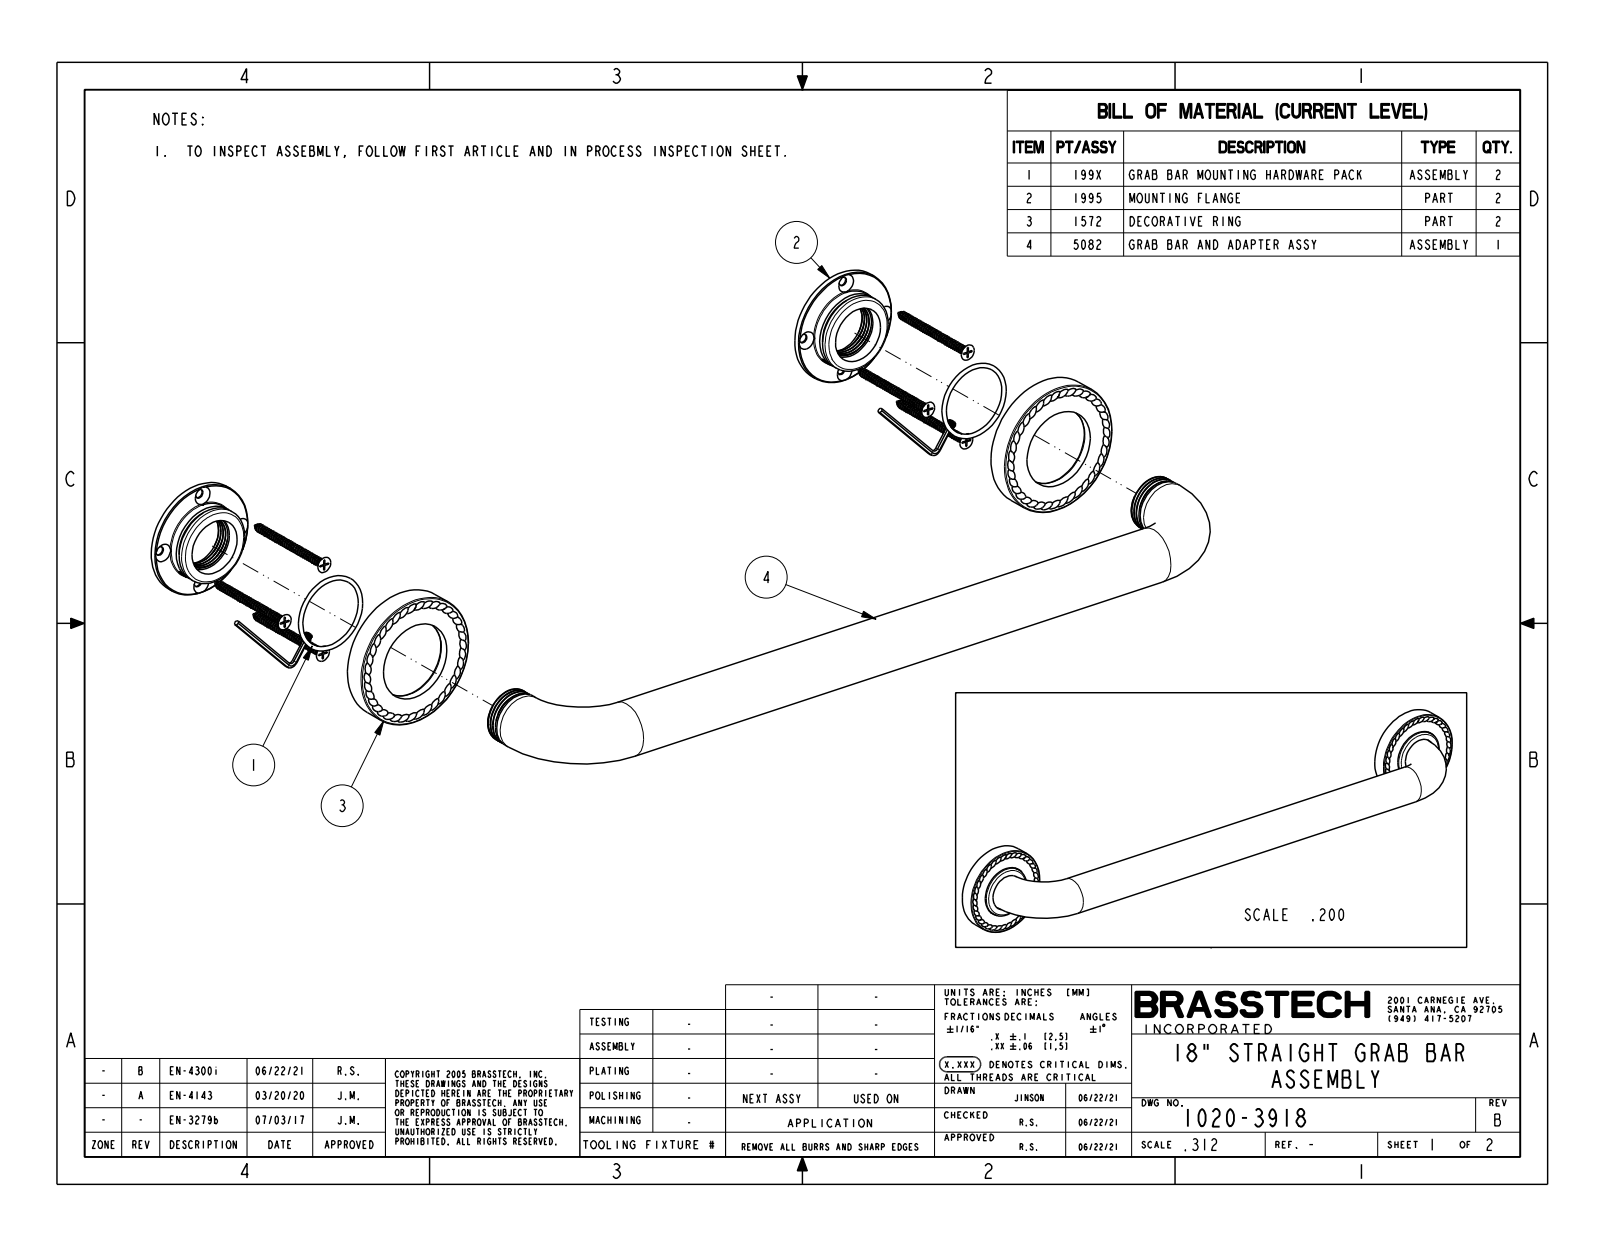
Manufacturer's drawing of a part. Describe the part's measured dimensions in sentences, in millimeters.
The part is named "1020-3918". Its 3-D file was written by "CREO PARAMETRIC BY PTC INC, 2018400 (CONFIG_CONTROL_DESIGN)". It is 1 solid with 106 faces: 8 planar, 10 cylindrical and 88 other. Overall it measures 533.4 by 76.2 by 69.9 millimeters. Its volume is 520 300 cubic millimeters and its surface area 73 550 square millimeters. Round bosses or shafts: 2 of diameter 76.2, 2 of diameter 44.5, 1 of diameter 31.8. The main face-to-face distances are 12.7, 15.2, 2.5.
